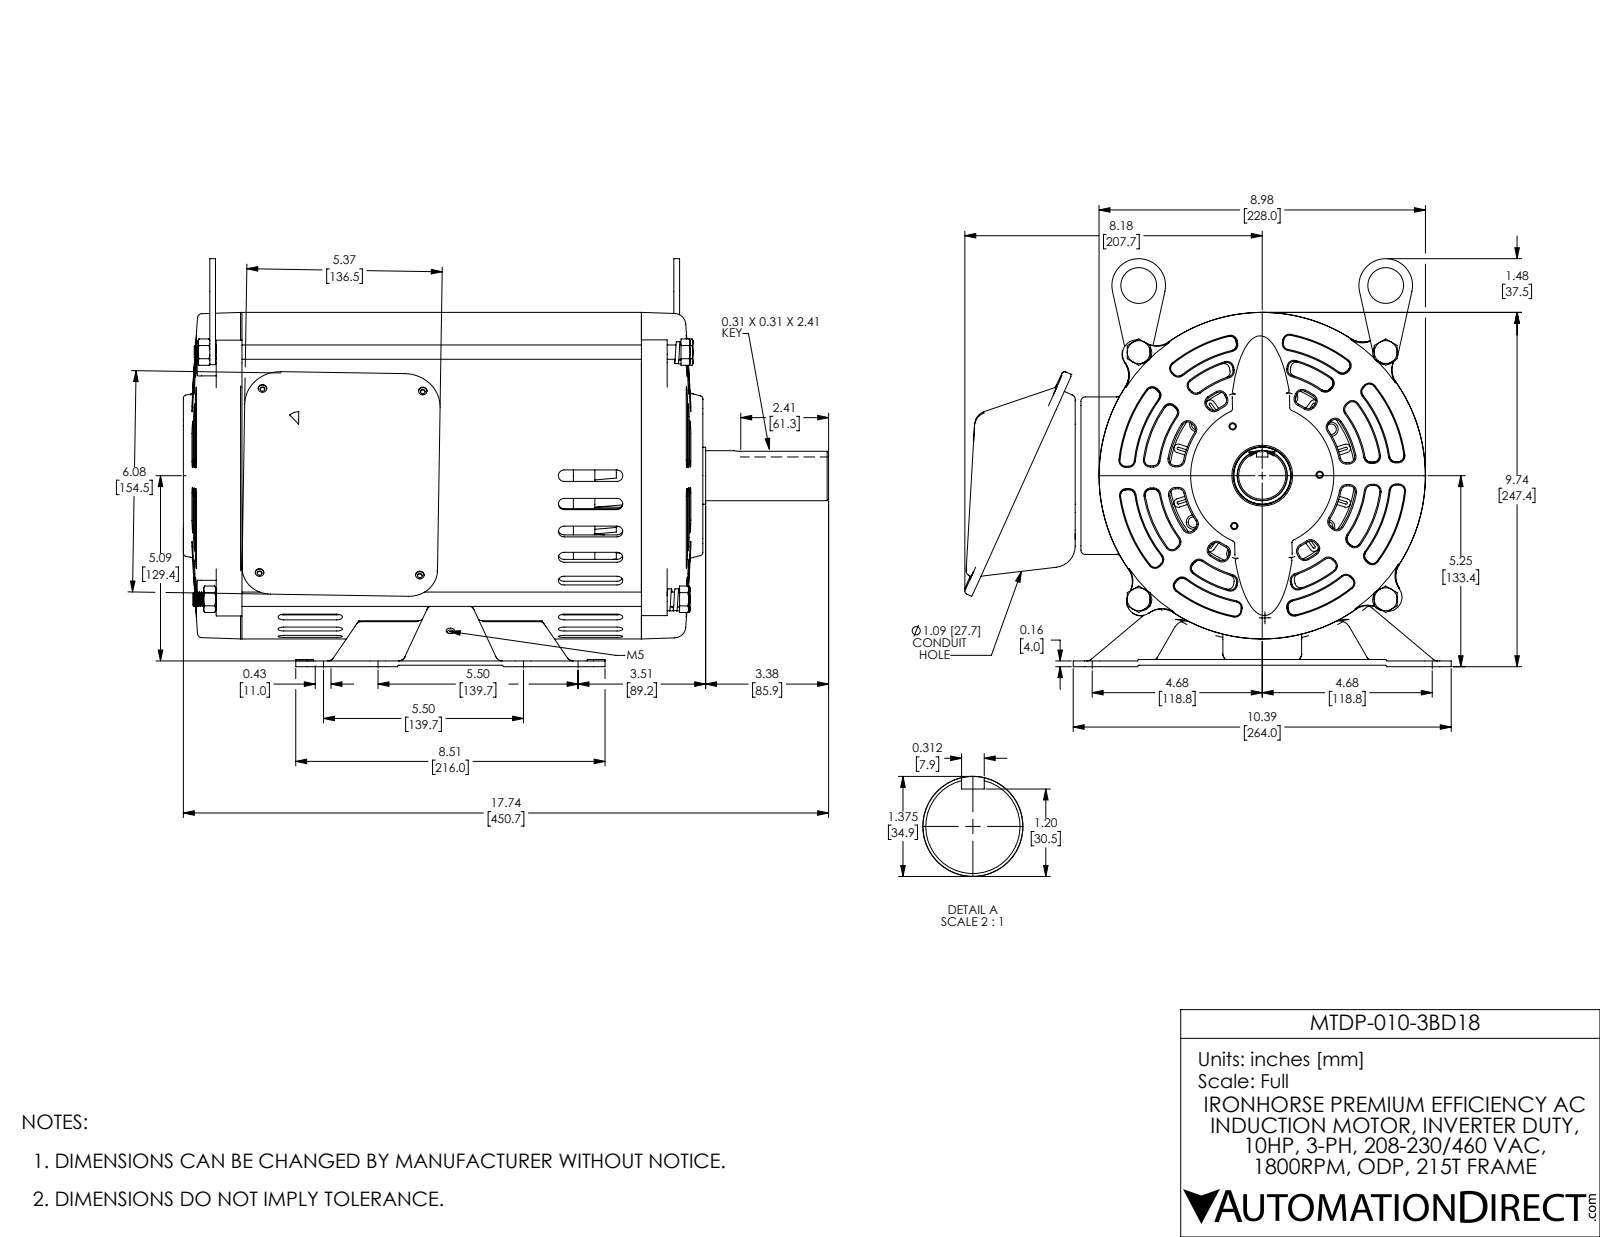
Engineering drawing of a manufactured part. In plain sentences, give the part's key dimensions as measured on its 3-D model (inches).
The part is named "ODP-213(5)T from XT Elec box fillet Surfacefix 1aR1b NEW ext cmod A". Its 3-D file was written by "SolidWorks 2017 (AUTOMOTIVE_DESIGN)". It is 21 solids with 2979 faces: 728 planar, 1064 cylindrical and 1187 other. Overall it measures 17.742 by 13.375 by 11.215 inches. Its volume is 328.2 cubic inches and its surface area 1 845 square inches. Round holes: 12 of diameter 0.13, 8 of diameter 0.413, 8 of diameter 0.433, 4 of diameter 0.236, 4 of diameter 0.268, 4 of diameter 0.394, 4 of diameter 0.402, 4 of diameter 0.458, 3 of diameter 0.15, 3 of diameter 0.165, 2 of diameter 0.354, 2 of diameter 0.984. Round bosses or shafts: 4 of diameter 0.606, 4 of diameter 0.394, 4 of diameter 0.33, 1 of diameter 8.976, 1 of diameter 5.287, 1 of diameter 4.331, 1 of diameter 3.622, 1 of diameter 1.732. Partial cylindrical surfaces (rounded edges, fillets, slot ends): 82 of radius 0.157, 62 of radius 0.079, 36 of radius 0.118, 33 of radius 0.354, 29 of radius 0.394, 28 of radius 0.039, 28 of radius 0.197, 13 of radius 0.315. The main face-to-face distances are 0.039, 0.157, 0.118, 0.197, 10.843, 0.039, 1.28, 1.138, 0.768, 0.354. The hole center spacings are 6.793, 3.15, 5.551, 7.089, 8.064, 6.792, 8.06, 1.5.
